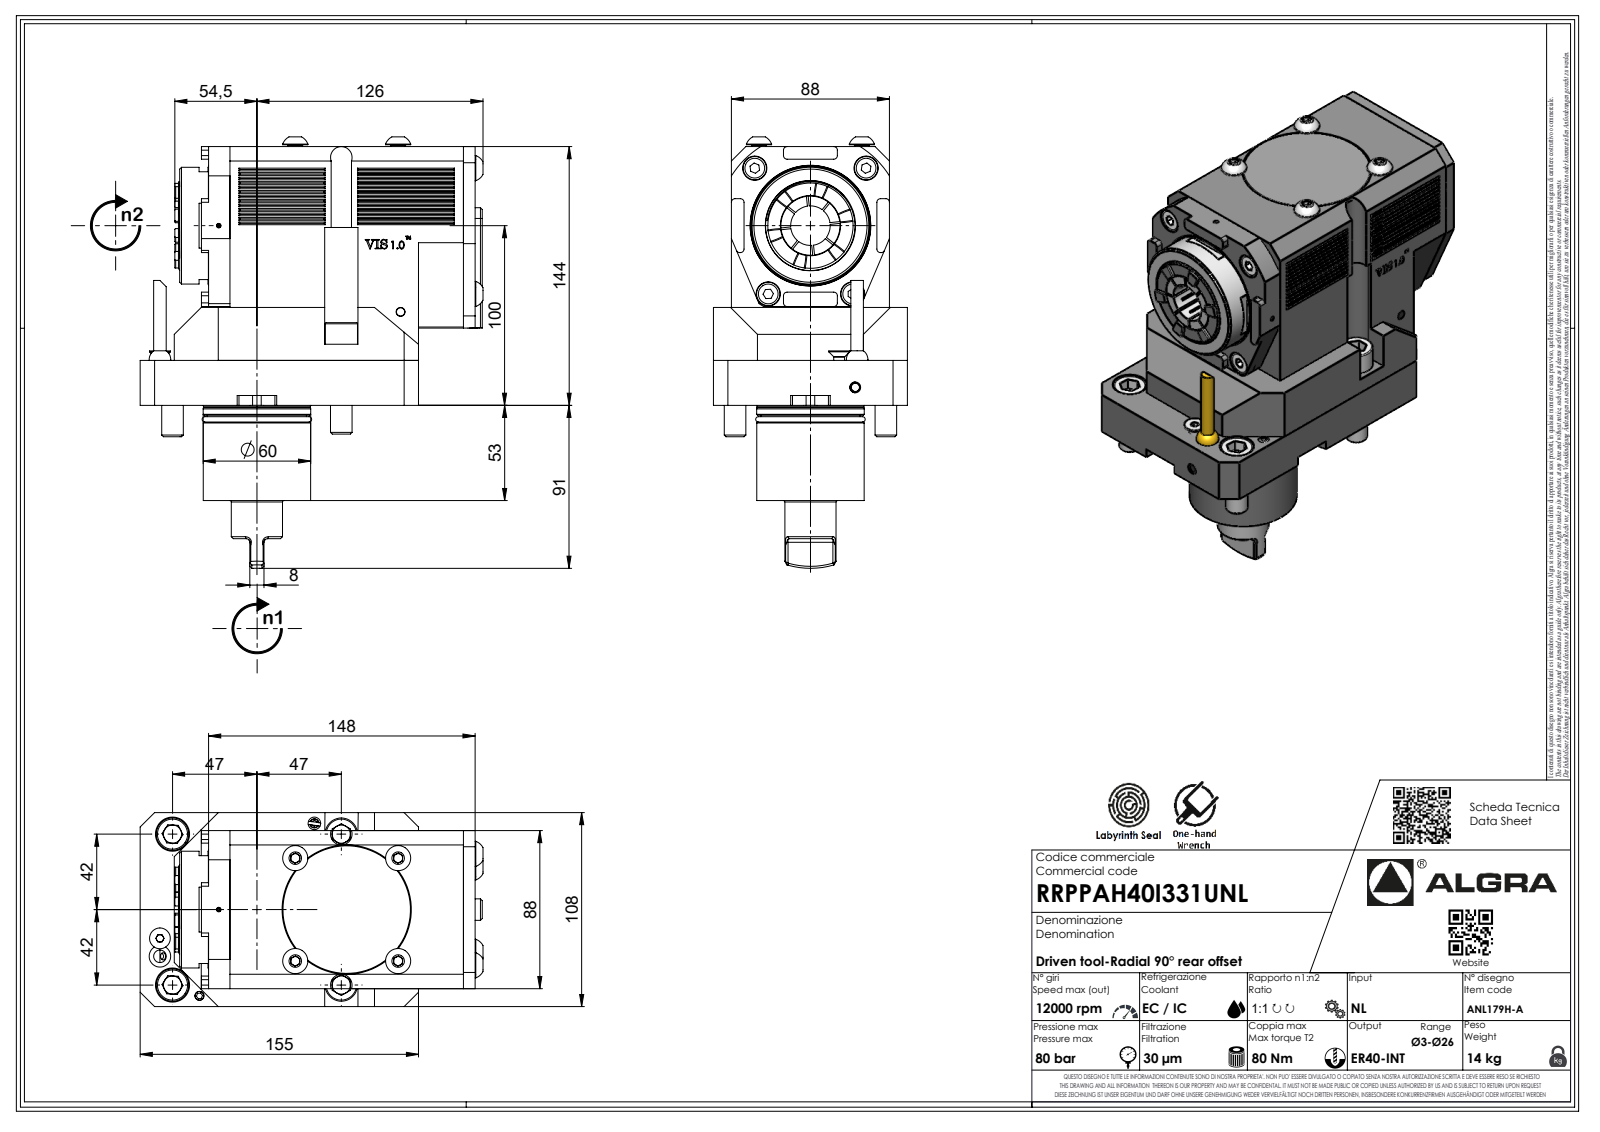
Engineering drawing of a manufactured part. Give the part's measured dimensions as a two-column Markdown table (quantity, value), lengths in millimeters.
| quantity | value |
| --- | --- |
| part name | RRPPAH40I331UNL |
| STEP written by | SolidWorks 2023 (AUTOMOTIVE_DESIGN) |
| units | millimeters |
| bodies | 1 solid, 694 faces (479 planar, 93 cylindrical, 122 other) |
| overall size | 240.1 × 190.9 × 108 |
| volume | 2 173 000 mm³ |
| surface area | 136 972 mm² |
| round holes (diameter × count) | 2.1 × 1, 12 × 1, 12.5 × 1 |
| round bosses / shafts (diameter × count) | 14 × 8, 8 × 4, 12 × 3, 18 × 2, 65 × 1, 59.9 × 1, 59.8 × 1, 59.5 × 1 |
| partial cylindrical surfaces (radius × count) | 2 × 22, 0.33 × 7, 0.52 × 7, 3.7 × 7, 1 × 2, 9.25 × 2, 0.21 × 1, 6 × 1 |
| main face-to-face distances | 98, 10, 144, 88, 108, 31.5, 164.5, 133, 54.5, 89.5 |
| hole center spacings | 84 |
